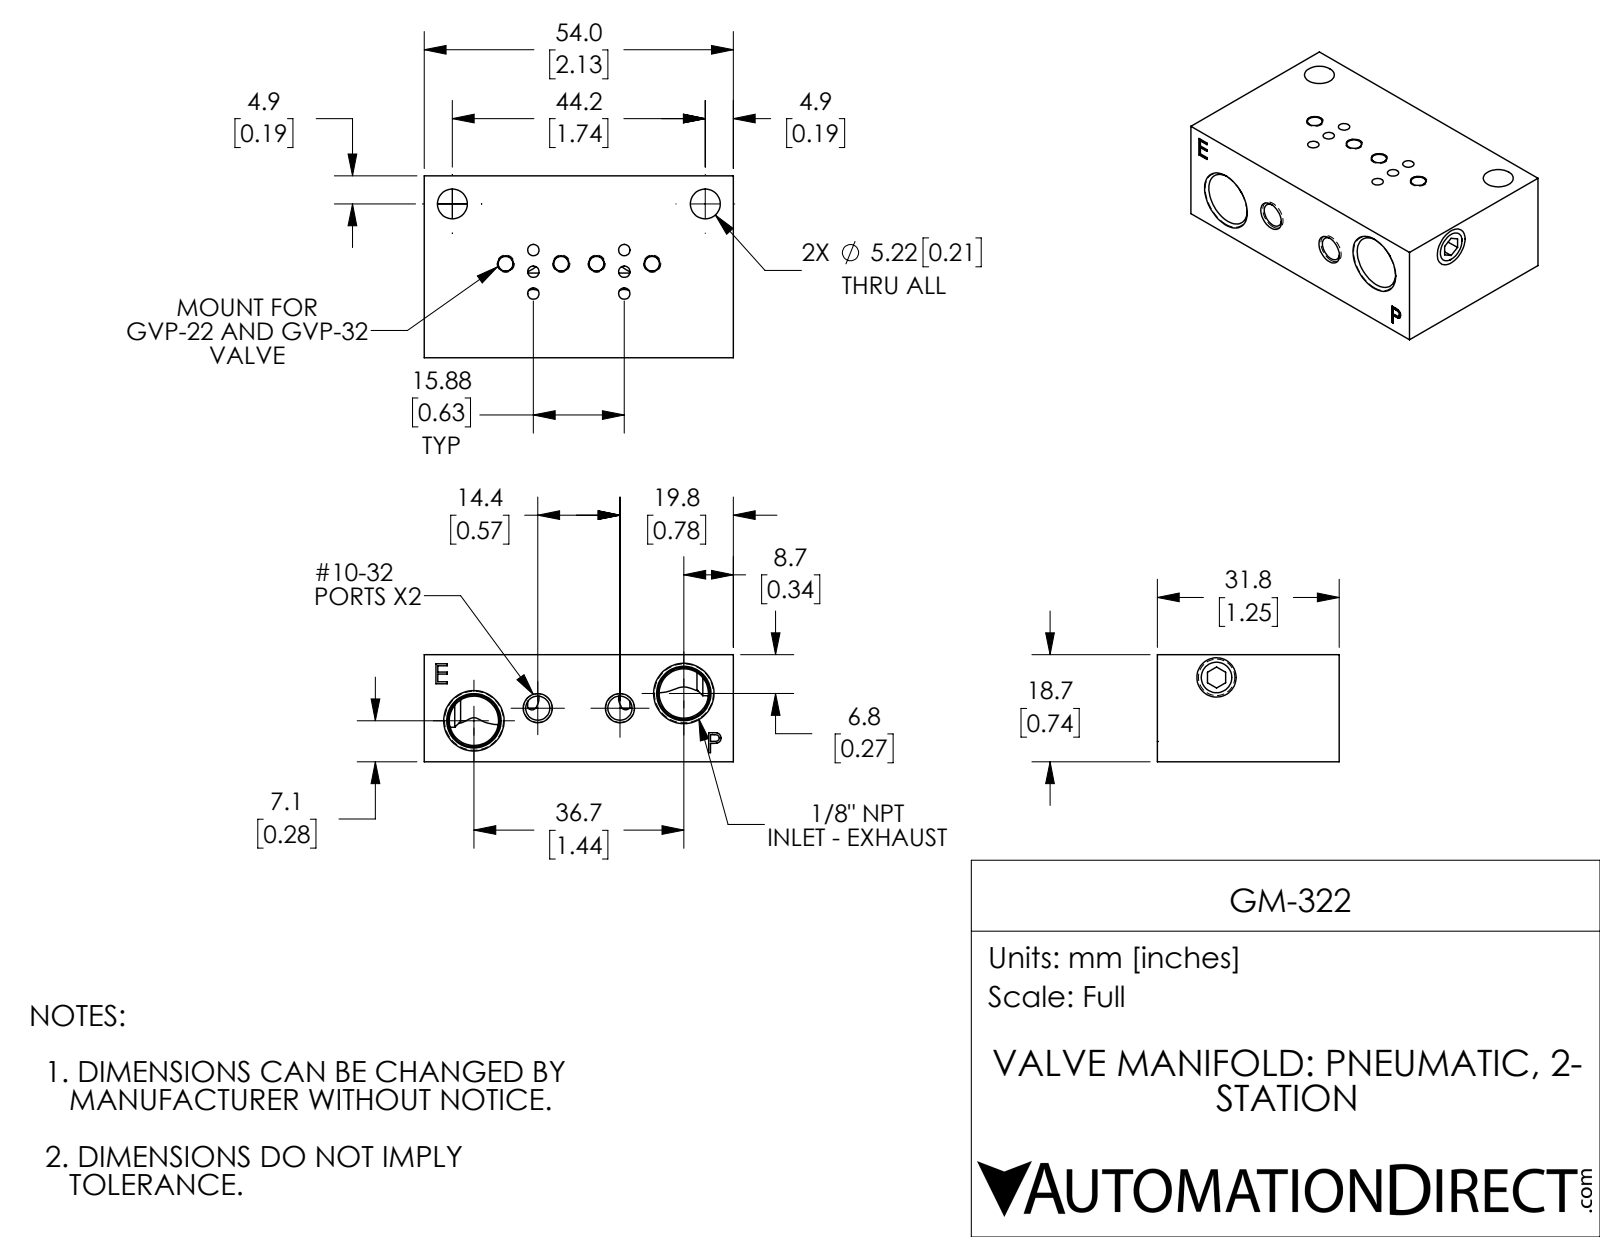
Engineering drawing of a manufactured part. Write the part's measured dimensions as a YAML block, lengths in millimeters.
part_name: "GM-322"
step_written_by: "SolidWorks 2018 (AUTOMOTIVE_DESIGN)"
units: millimeters
bodies: {solids: 3, faces: 158, planar: 49, cylindrical: 41, other: 68}
overall_size: [54, 31.8, 18.7]
volume: 27280
surface_area: 10200
round_holes:
  - {diameter: 2, count: 6}
  - {diameter: 2.6, count: 4}
  - {diameter: 4.2, count: 2}
  - {diameter: 5.2, count: 2}
  - {diameter: 5.4, count: 2}
  - {diameter: 8.6, count: 2}
round_bosses_or_shafts:
  - {diameter: 6.4, count: 2}
face_to_face_distances: [18.7, 31.8, 54, 3.2, 47.6, 6.4, 4.1, 49.9, 2.3, 43.6]
hole_center_spacings: [5.1, 15.9, 5.4, 7.1, 3.8, 3.8, 7.6, 11.1]
